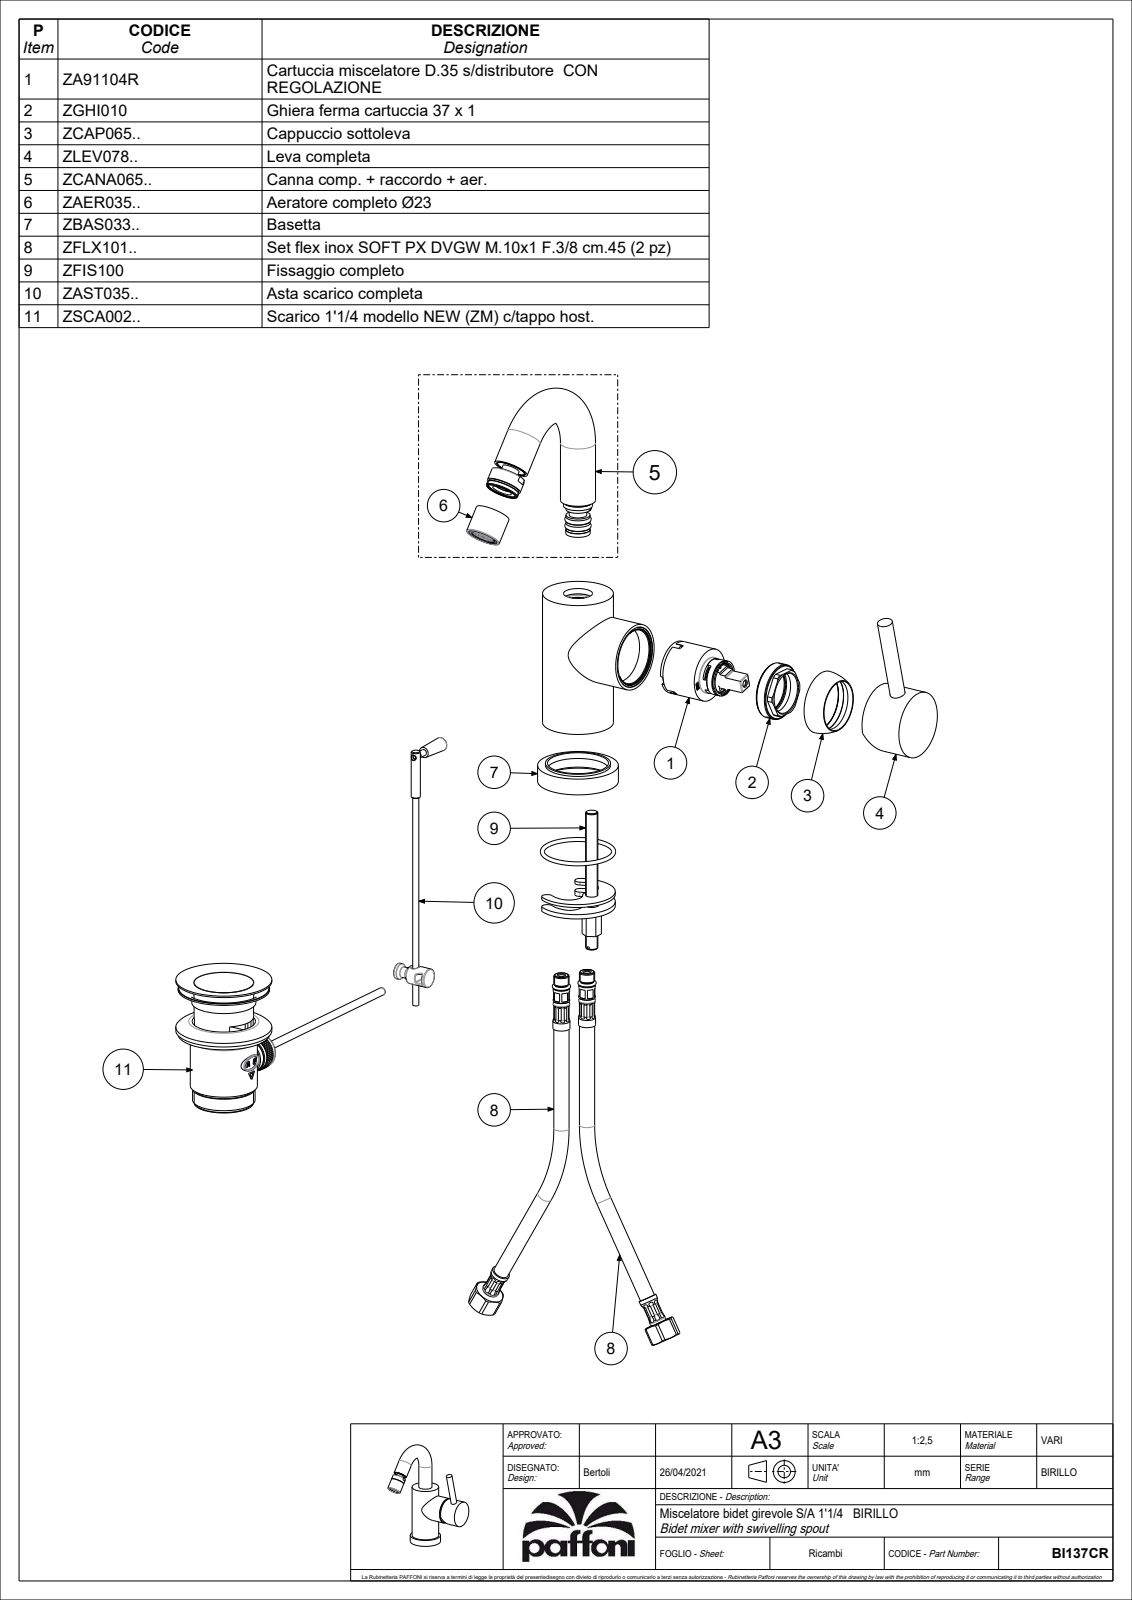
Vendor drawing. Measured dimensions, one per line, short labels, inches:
name: BI137CR
written by: CREO PARAMETRIC BY PTC INC, 2020044 (CONFIG_CONTROL_DESIGN)
unit: in
bodies: 4 solids, 1192 faces (655 planar, 326 cylindrical, 211 other)
size: 7.386 × 5.844 × 4.108
volume: 11.68 in³; area: 153.6 in²
holes: 3× ⌀0.13, 3× ⌀0.256, 3× ⌀0.354, 3× ⌀0.709, 3× ⌀0.748, 2× ⌀0.157, 2× ⌀0.217, 2× ⌀0.394, 2× ⌀0.433, 2× ⌀1.575, 1× ⌀0.197, 1× ⌀0.268
bosses: 3× ⌀0.906, 2× ⌀0.157, 1× ⌀2.087, 1× ⌀1.831, 1× ⌀1.732, 1× ⌀1.681, 1× ⌀1.449, 1× ⌀1.378
rounds: 27× R0.02, 11× R0.006, 4× R0.012, 2× R0.039, 2× R0.089, 1× R0.041, 1× R0.083, 1× R0.167
face distances: 0.354, 2.953, 0.059, 0.591, 0.945, 0.079, 2.217, 0.433, 1.004, 0.02
hole spacings: 0.432, 0.804, 0.047, 0.197, 0.361, 0.365, 0.401, 0.419
